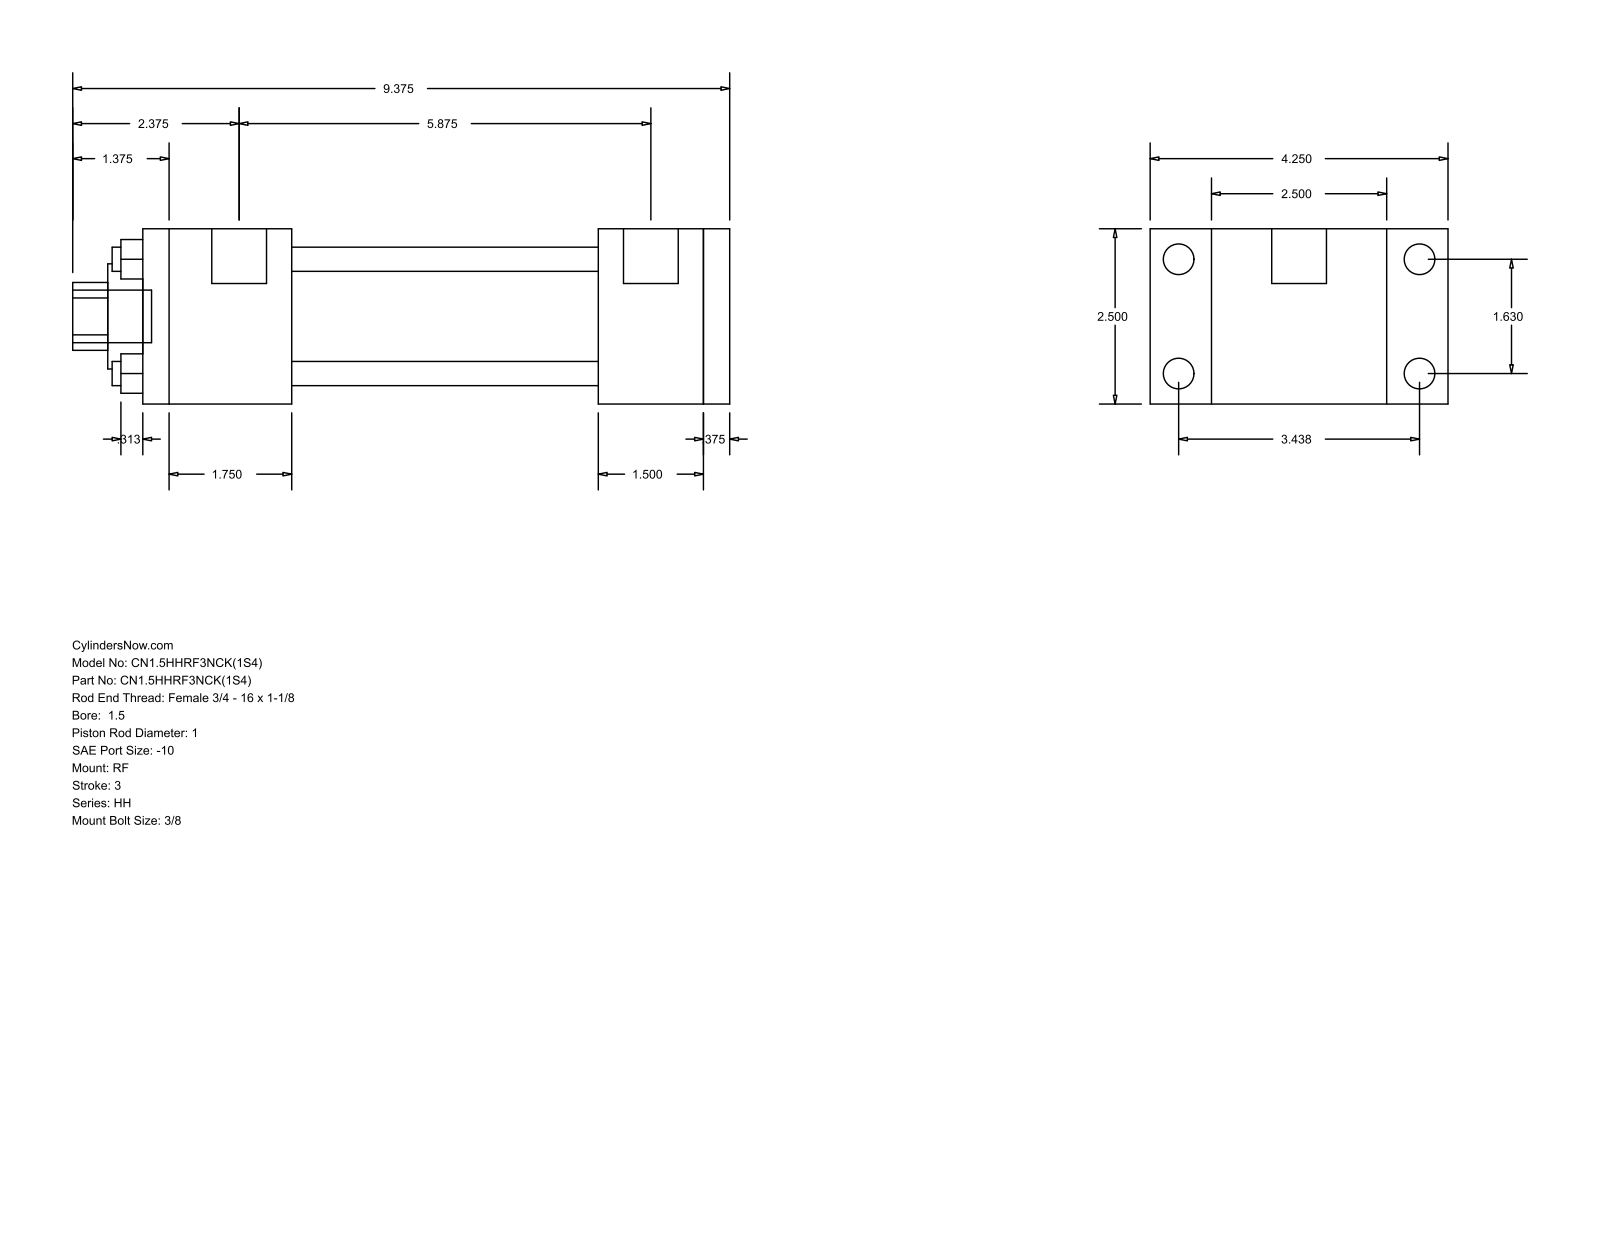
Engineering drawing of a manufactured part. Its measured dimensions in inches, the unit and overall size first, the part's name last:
Units: inches
Overall size (bounding box): 9.375 × 4.25 × 2.5
Round holes (diameter × count): ⌀0.345 ×4, ⌀1 ×1, ⌀1.5 ×1, ⌀1.75 ×1
Round bosses / shafts (diameter × count): ⌀0.438 ×4, ⌀0.219 ×4, ⌀0.781 ×2, ⌀0.75 ×1
Partial cylindrical surfaces — rounded edges, fillets, slot ends (radius × count): R0.484 ×1
Main face-to-face distances: 2.5, 0.375, 4.375, 5.875, 6.25, 1.5, 1.875, 2.125, 6.5, 8
Hole centre spacings: 1.152, 1.63, 2.305
Bodies: 0 solids, 92 faces (64 planar, 28 cylindrical, 0 other)
Part name (STEP PRODUCT): HH_RF__0150_1
STEP written by: GSSL Pune (CONFIG_CONTROL_DESIGN)
